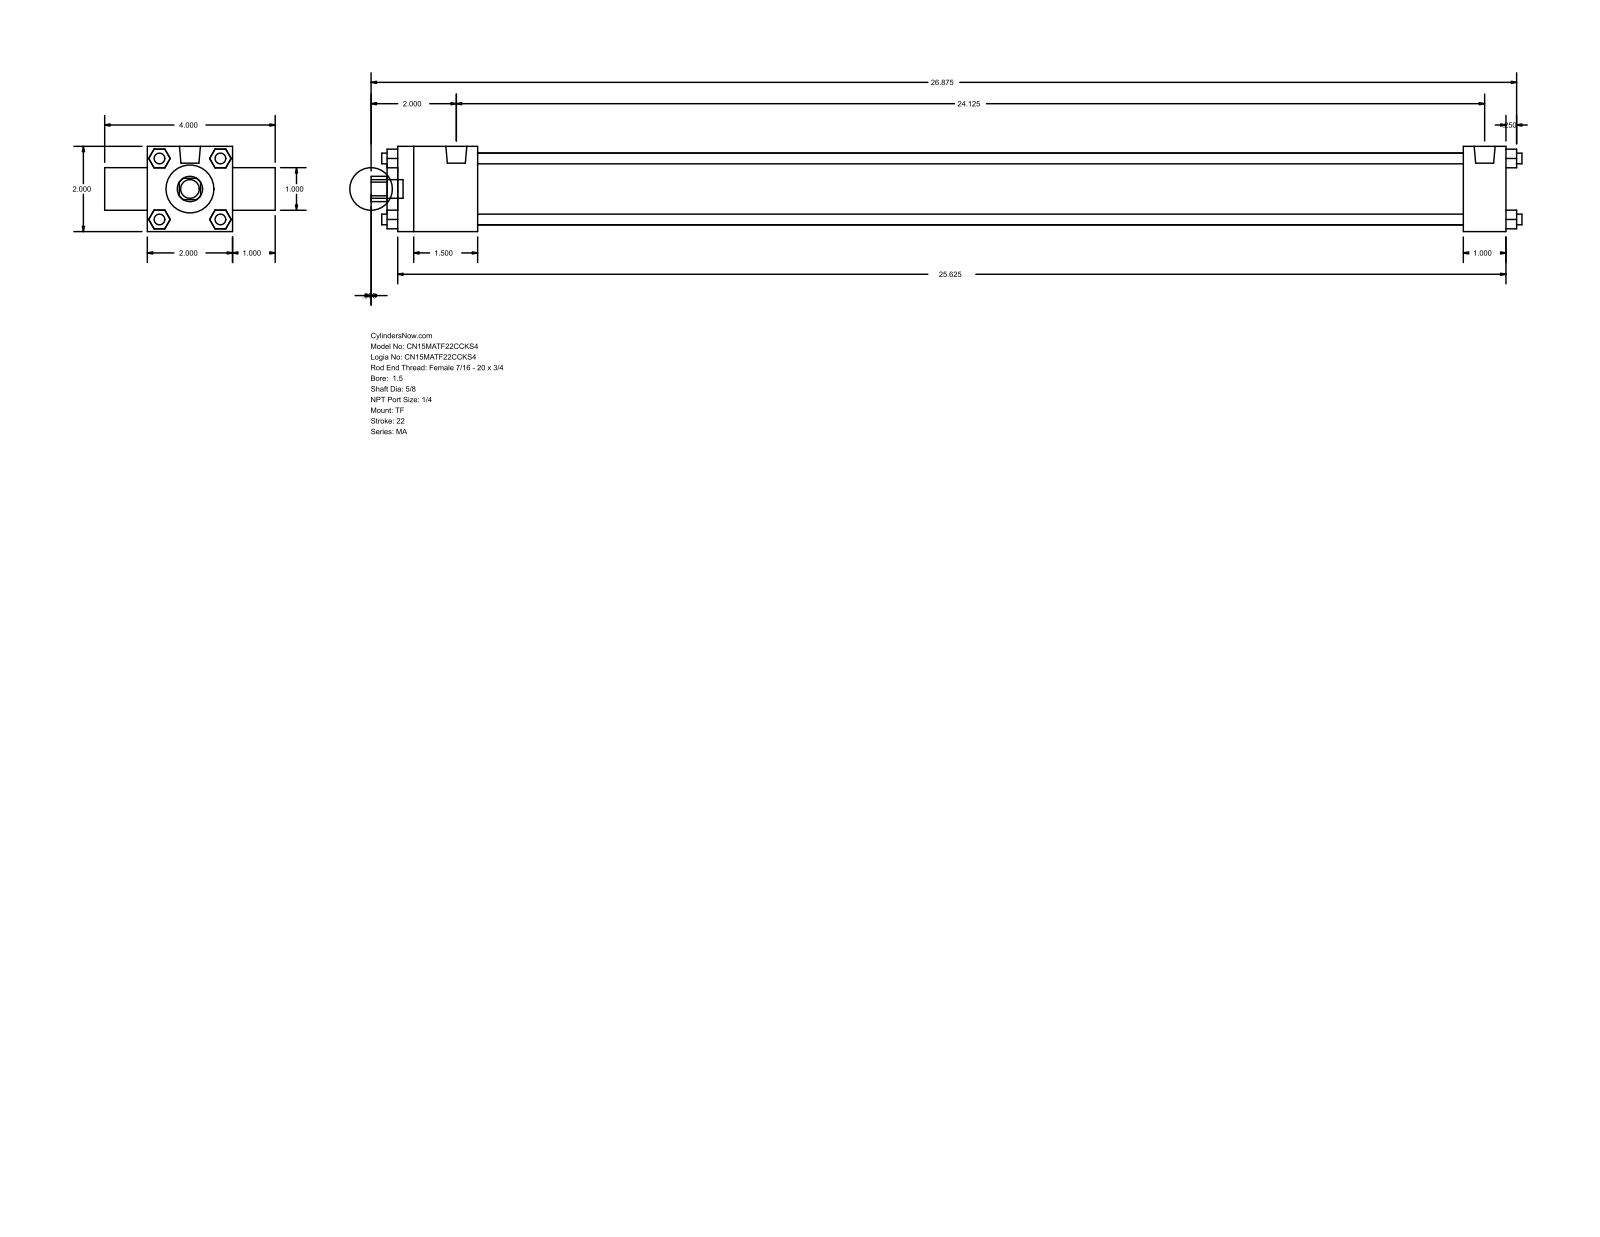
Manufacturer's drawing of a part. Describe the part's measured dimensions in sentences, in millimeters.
The part is named "MA_TF__0150_0.625". Its 3-D file was written by "GSSL Pune (CONFIG_CONTROL_DESIGN)". It is 0 solids with 120 faces: 92 planar, 28 cylindrical and 0 other. Overall it measures 685.8 by 101.6 by 50.8 millimeters. Round holes: 1 of diameter 15.88, 1 of diameter 25.4, 1 of diameter 28.57, 1 of diameter 42.93. Round bosses or shafts: 4 of diameter 6.35, 3 of diameter 7.94, 2 of diameter 12.49, 1 of diameter 11.11. Partial cylindrical surfaces (rounded edges, fillets, slot ends): 1 of radius 7.54. The main face-to-face distances are 50.8, 660.39, 6.35, 666.74, 25.4, 76.2, 47.62, 635, 587.38, 612.77.
